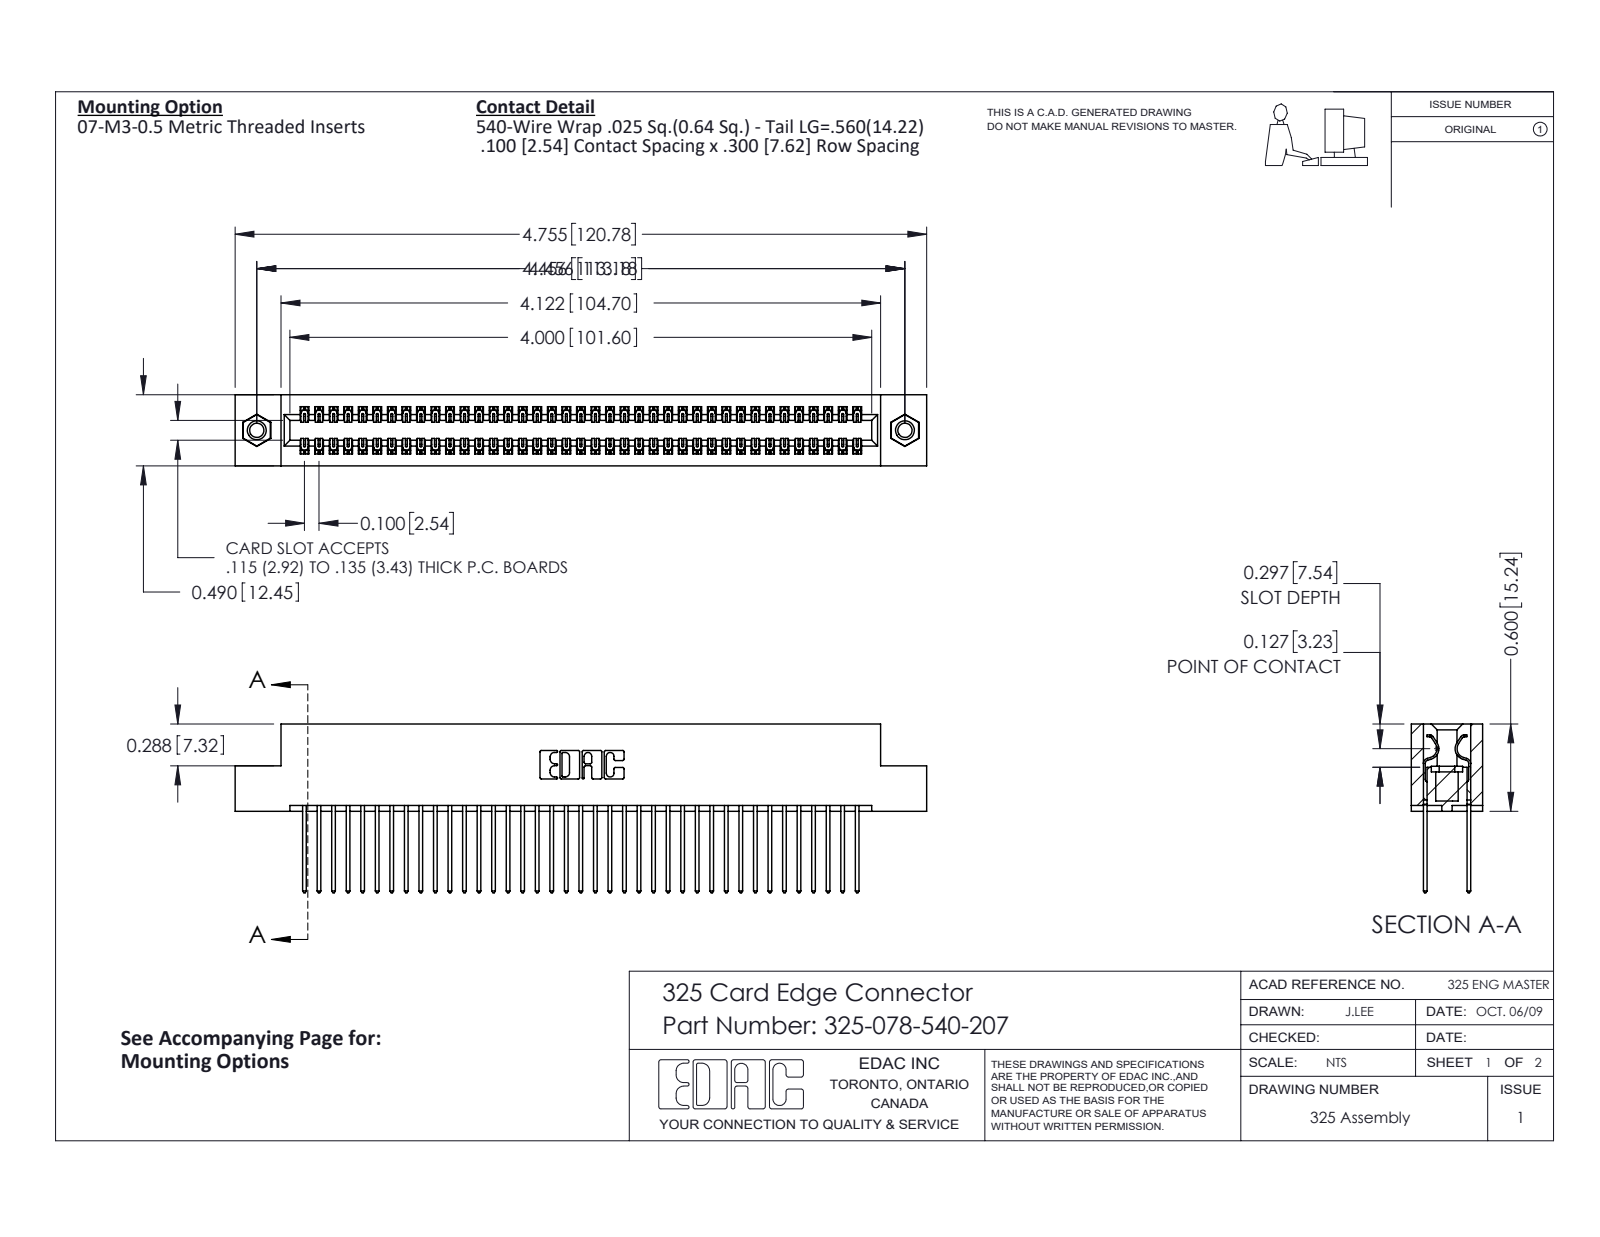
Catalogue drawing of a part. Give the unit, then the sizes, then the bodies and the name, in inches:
Units: inches
Overall size (bounding box): 4.755 × 1.16 × 0.49
Round holes (diameter × count): ⌀0.098 ×2, ⌀0.125 ×2, ⌀0.16 ×2
Round bosses / shafts (diameter × count): ⌀0.155 ×2
Partial cylindrical surfaces — rounded edges, fillets, slot ends (radius × count): R0.006 ×117, R0.01 ×78, R0.01 ×22, R0.007 ×6, R0.031 ×6, R0.026 ×3, R0.014 ×2, R0.022 ×2
Main face-to-face distances: 0.083, 0.407, 0.3, 0.107, 0.383, 0.025, 0.49, 0.325, 0.275, 0.56
Hole centre spacings: 4.456
Volume: 0.967 in³ · Surface area: 31.84 in²
Bodies: 81 solids, 4230 faces (2910 planar, 1304 cylindrical, 16 other)
Part name (STEP PRODUCT): 325-292-001_325-293-140; 325 Part_TI; 325-078-540-207; 345-250-001_345-250-005-103
STEP written by: SolidWorks 2016 (CONFIG_CONTROL_DESIGN)
